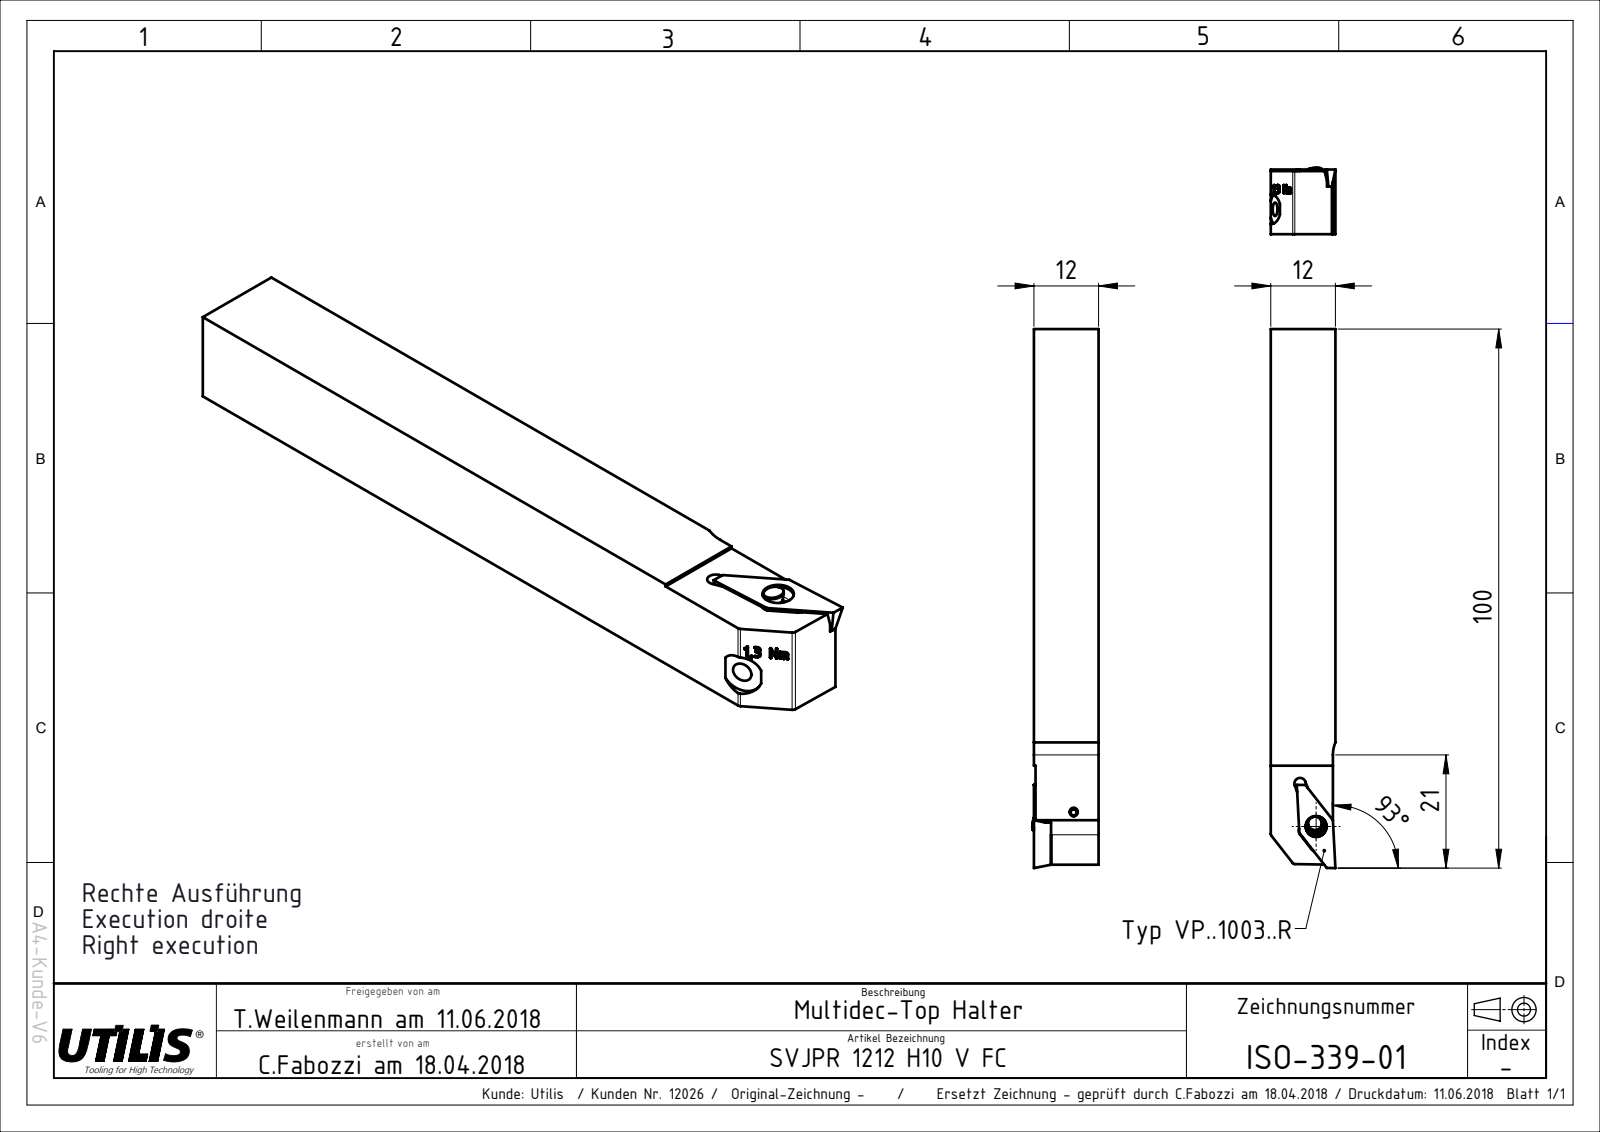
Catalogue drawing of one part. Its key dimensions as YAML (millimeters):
part_name: "ISO-339-01"
step_written_by: "SolidWorks 2018 (AUTOMOTIVE_DESIGN)"
units: millimeters
bodies: {solids: 1, faces: 110, planar: 58, cylindrical: 8, other: 44}
overall_size: [100, 12, 12]
volume: 13952
surface_area: 5088
partial_cylinders:
  - {radius: 1.05, count: 3}
  - {radius: 0.5, count: 2}
  - {radius: 6, count: 1}
  - {radius: 6.1, count: 1}
face_to_face_distances: [12, 11.53, 0.47, 11.7, 3.18, 2.88, 8.82, 4.32, 10.36, 6.04]
